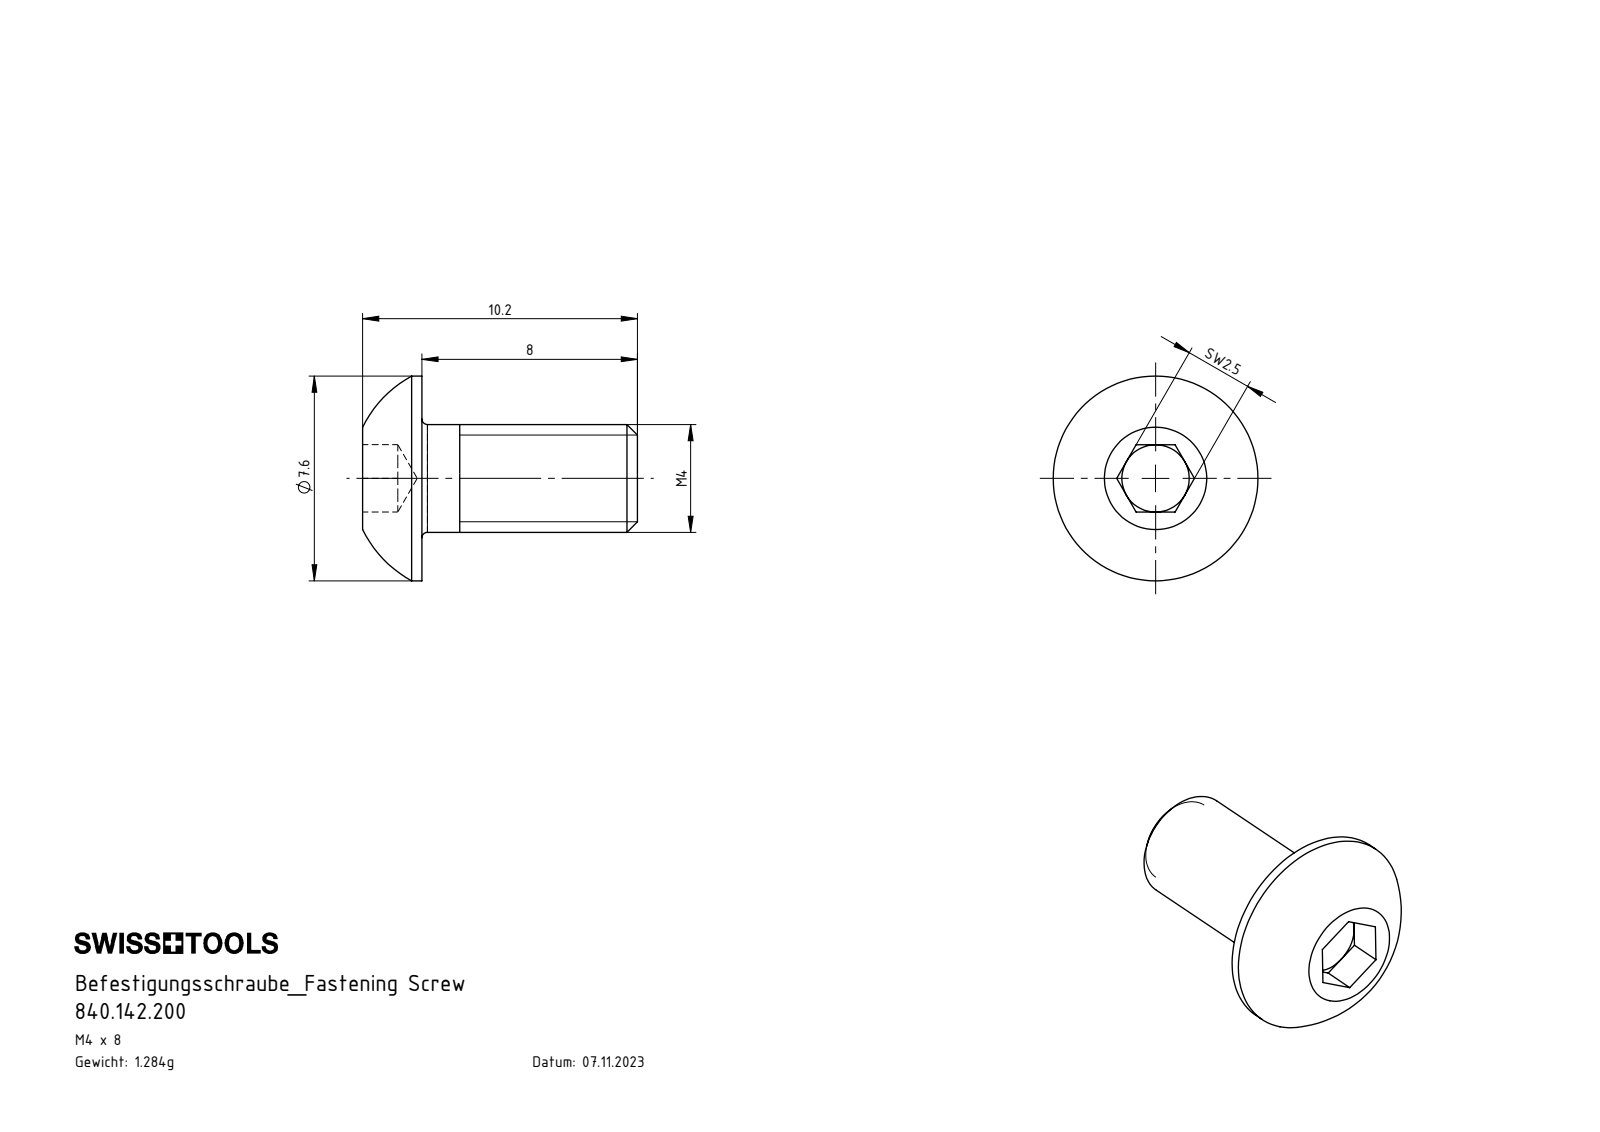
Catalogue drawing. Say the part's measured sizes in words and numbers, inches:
The part is named "840.142.200". Its 3-D file was written by "SolidWorks 2022 (AUTOMOTIVE_DESIGN)". It is 1 solid with 27 faces: 15 planar, 4 cylindrical and 8 other. Overall it measures 0.402 by 0.299 by 0.299 inches. Its volume is 0.01 cubic inches and its surface area 0.347 square inches. Round bosses or shafts: 1 of diameter 0.299, 1 of diameter 0.157. The main face-to-face distances are 0.315, 0.087, 0.402, 0.098, 0.051, 0.035, 0.35.
